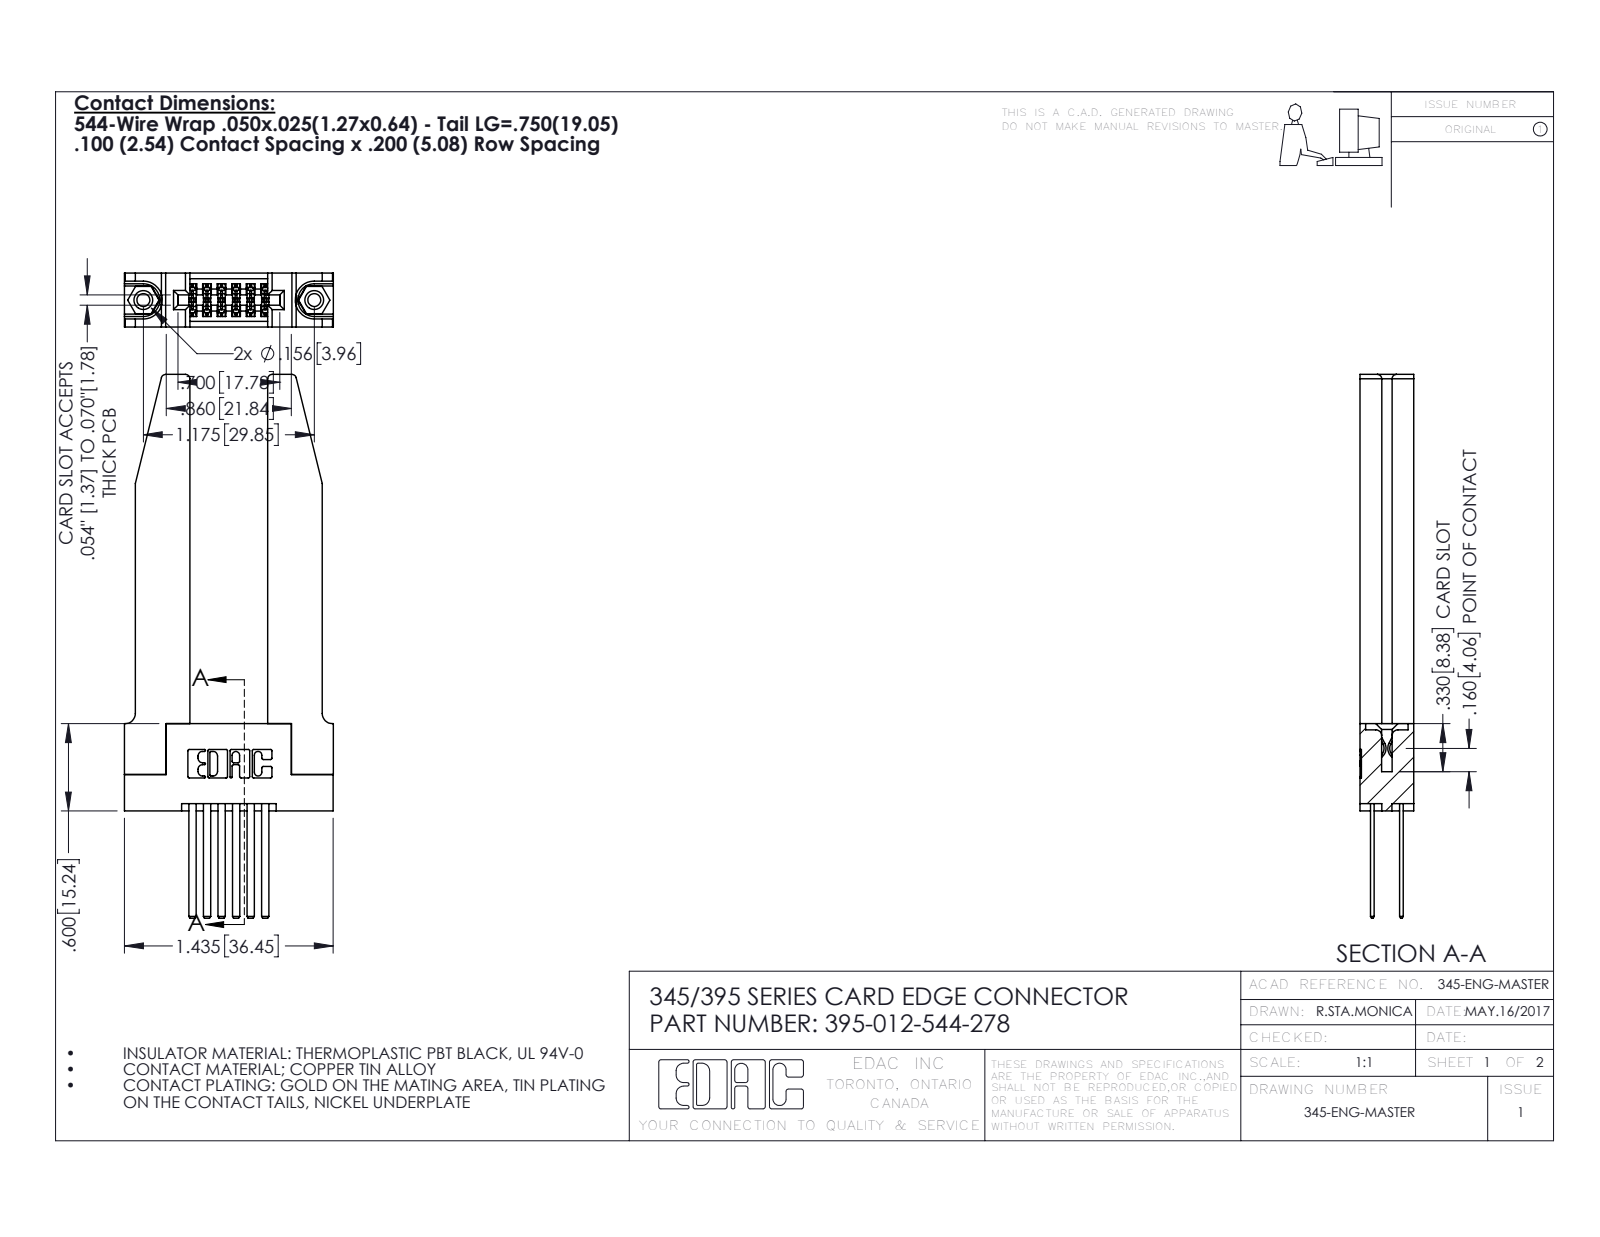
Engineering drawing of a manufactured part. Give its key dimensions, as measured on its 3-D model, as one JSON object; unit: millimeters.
{"part_name": "345-250-001_345-250-001-102; 345-220-078_345-220-078; 345 Part_Flush Mounting Lugs - 0.156 Dia-TH; 395-012-544-278 (+1 more)", "step_written_by": "SolidWorks 2016 (CONFIG_CONTROL_DESIGN)", "units": "millimeters", "bodies": {"solids": 17, "faces": 888, "planar": 570, "cylindrical": 266, "other": 52}, "overall_size": [94.9, 36.5, 9.4], "volume_mm3": 11100, "surface_area_mm2": 11630, "round_holes": [[2.3, 2], [3.2, 2], [4, 2], [1.6, 1]], "round_bosses_or_shafts": [[3.9, 2]], "partial_cylinders_radius": [[0.3, 22], [0.2, 18], [0.8, 8], [0.2, 6], [0.8, 6], [0.7, 3], [0.4, 2], [0.5, 2]], "face_to_face_distances": [9.4, 1.8, 7.6, 5.1, 3.8, 3.8, 2, 5.6, 2.5, 6.9], "hole_center_spacings": [6.9, 24, 29.8]}
